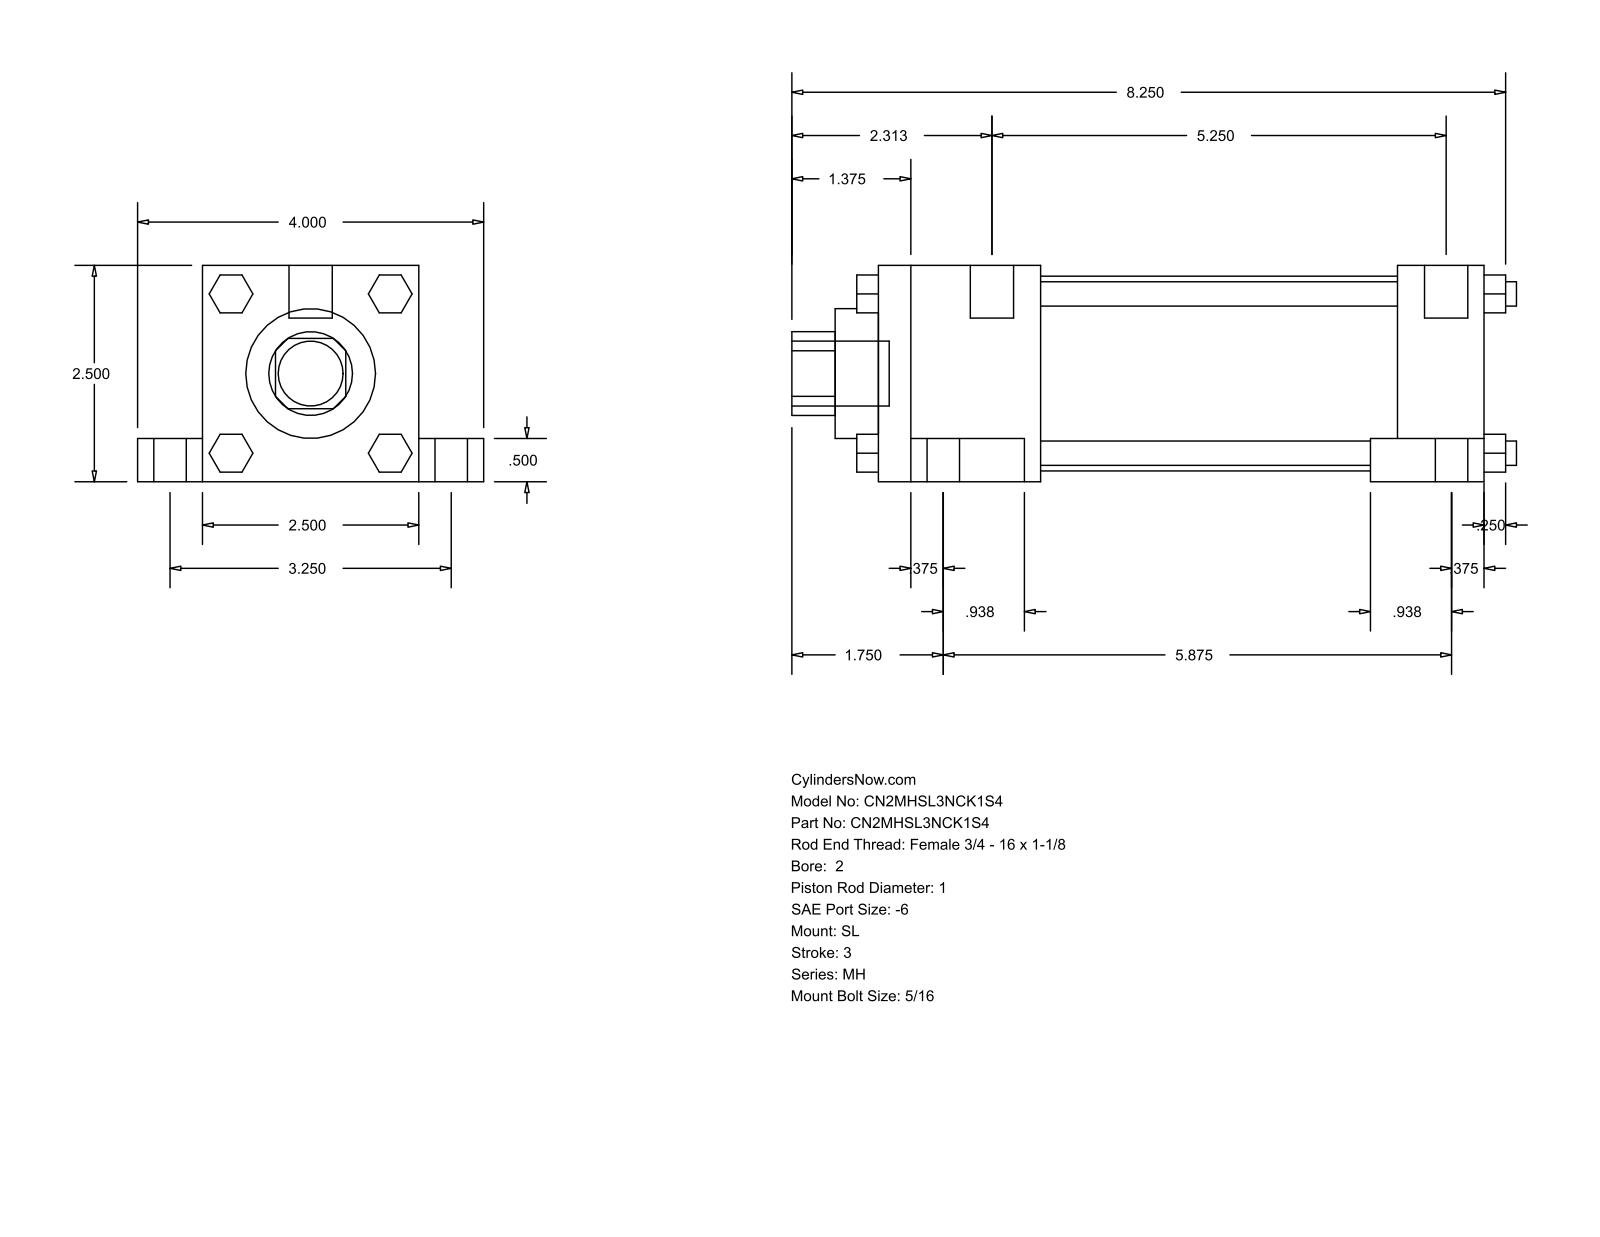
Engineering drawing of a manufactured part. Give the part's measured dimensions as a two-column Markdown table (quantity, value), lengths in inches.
| quantity | value |
| --- | --- |
| part name | MH_SL__0200_1 |
| STEP written by | GSSL Pune (CONFIG_CONTROL_DESIGN) |
| units | inches |
| bodies | 0 solids, 148 faces (112 planar, 36 cylindrical, 0 other) |
| overall size | 8.375 × 4 × 2.5 |
| round holes (diameter × count) | 1 × 1, 1.5 × 1, 2.25 × 1 |
| round bosses / shafts (diameter × count) | 0.625 × 4, 0.375 × 4, 0.281 × 4, 0.219 × 4, 0.5 × 2, 0.75 × 1 |
| partial cylindrical surfaces (radius × count) | 0.484 × 1 |
| main face-to-face distances | 2.5, 7, 0.5, 0.75, 2, 3.25, 0.375, 1, 4, 6 |
